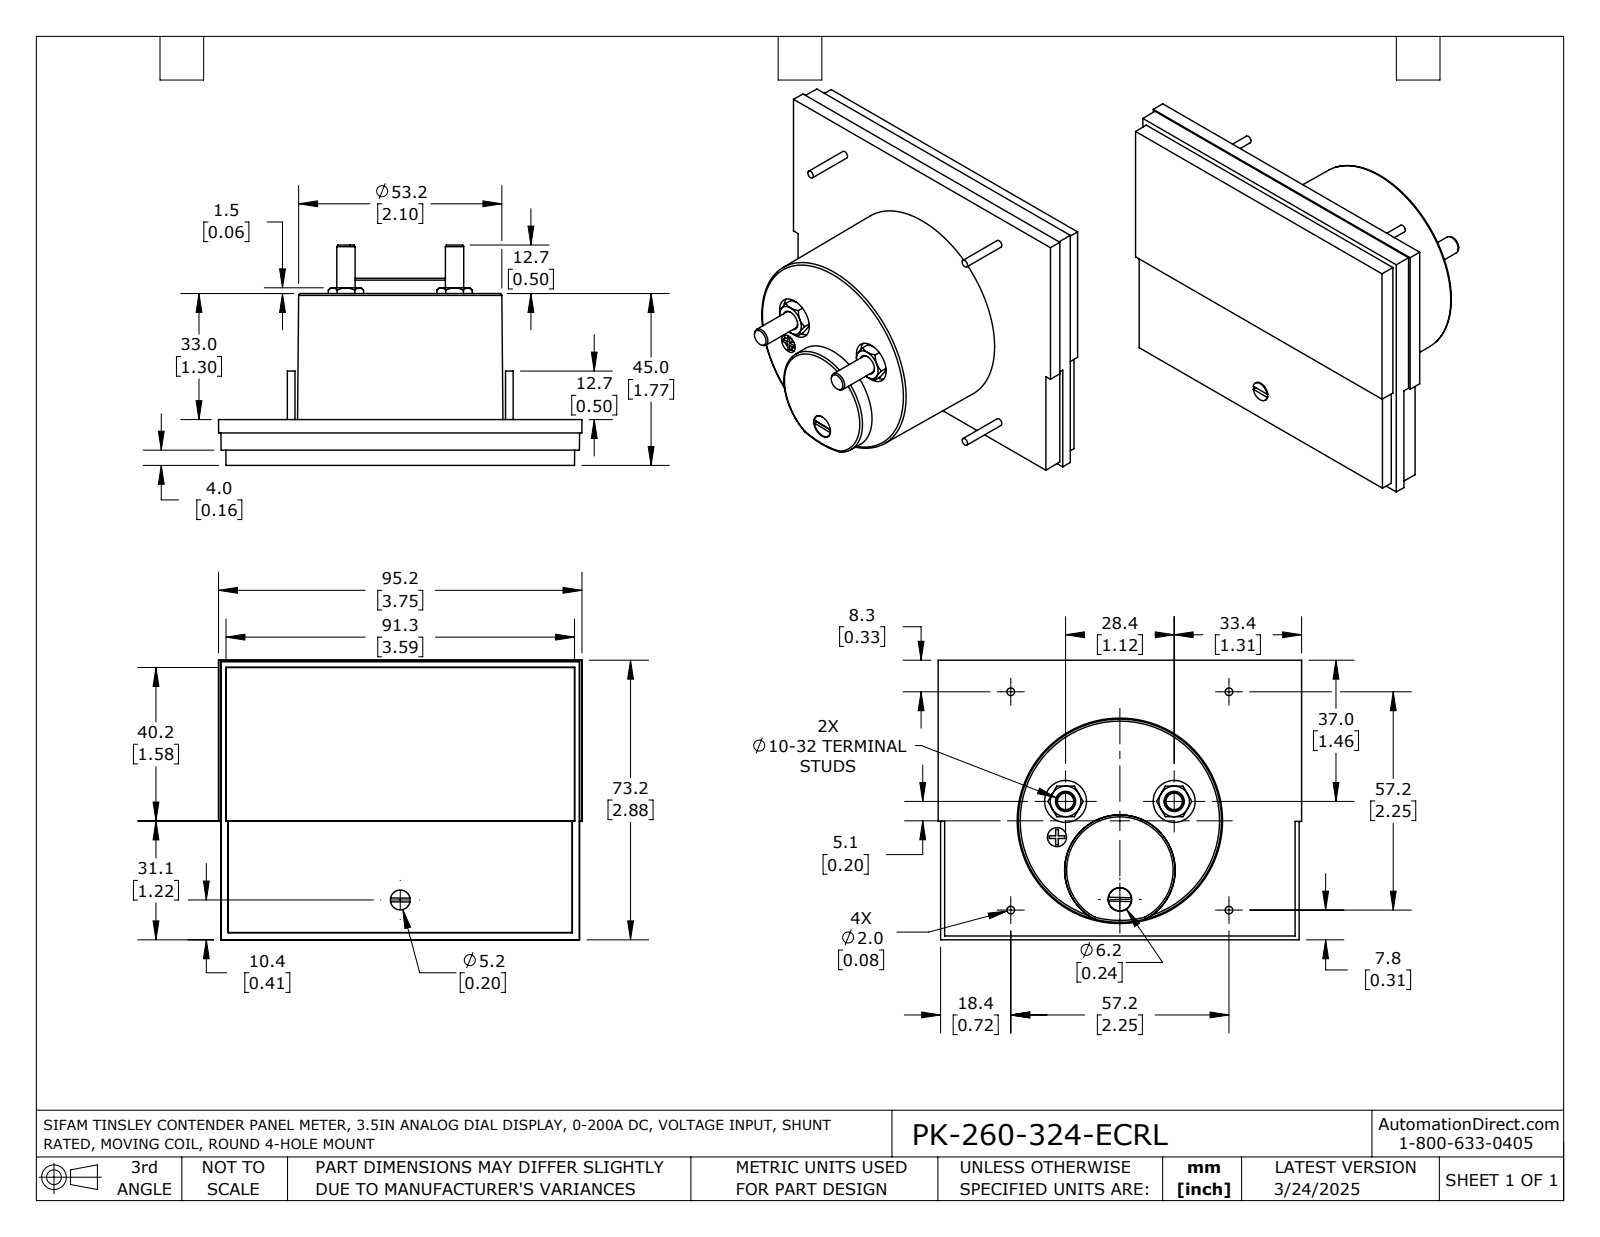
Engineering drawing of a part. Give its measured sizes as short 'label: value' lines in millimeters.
name: PK-260-324-ECRL
written by: SolidWorks 2021 (AUTOMOTIVE_DESIGN)
unit: mm
bodies: 1 solid, 163 faces (76 planar, 31 cylindrical, 56 other)
size: 95.2 × 73.2 × 57.7
volume: 154 800 mm³; area: 24 770 mm²
holes: 2× ⌀11, 1× ⌀5, 1× ⌀6.2
bosses: 4× ⌀2, 2× ⌀4.8, 1× ⌀6, 1× ⌀5.2
rounds: 1× R2.5
face distances: 12, 0.8, 11.3, 45, 33, 44.2, 4, 1.9, 8, 37
hole spacings: 29.3, 9.6, 23.2, 28.4, 32.1
